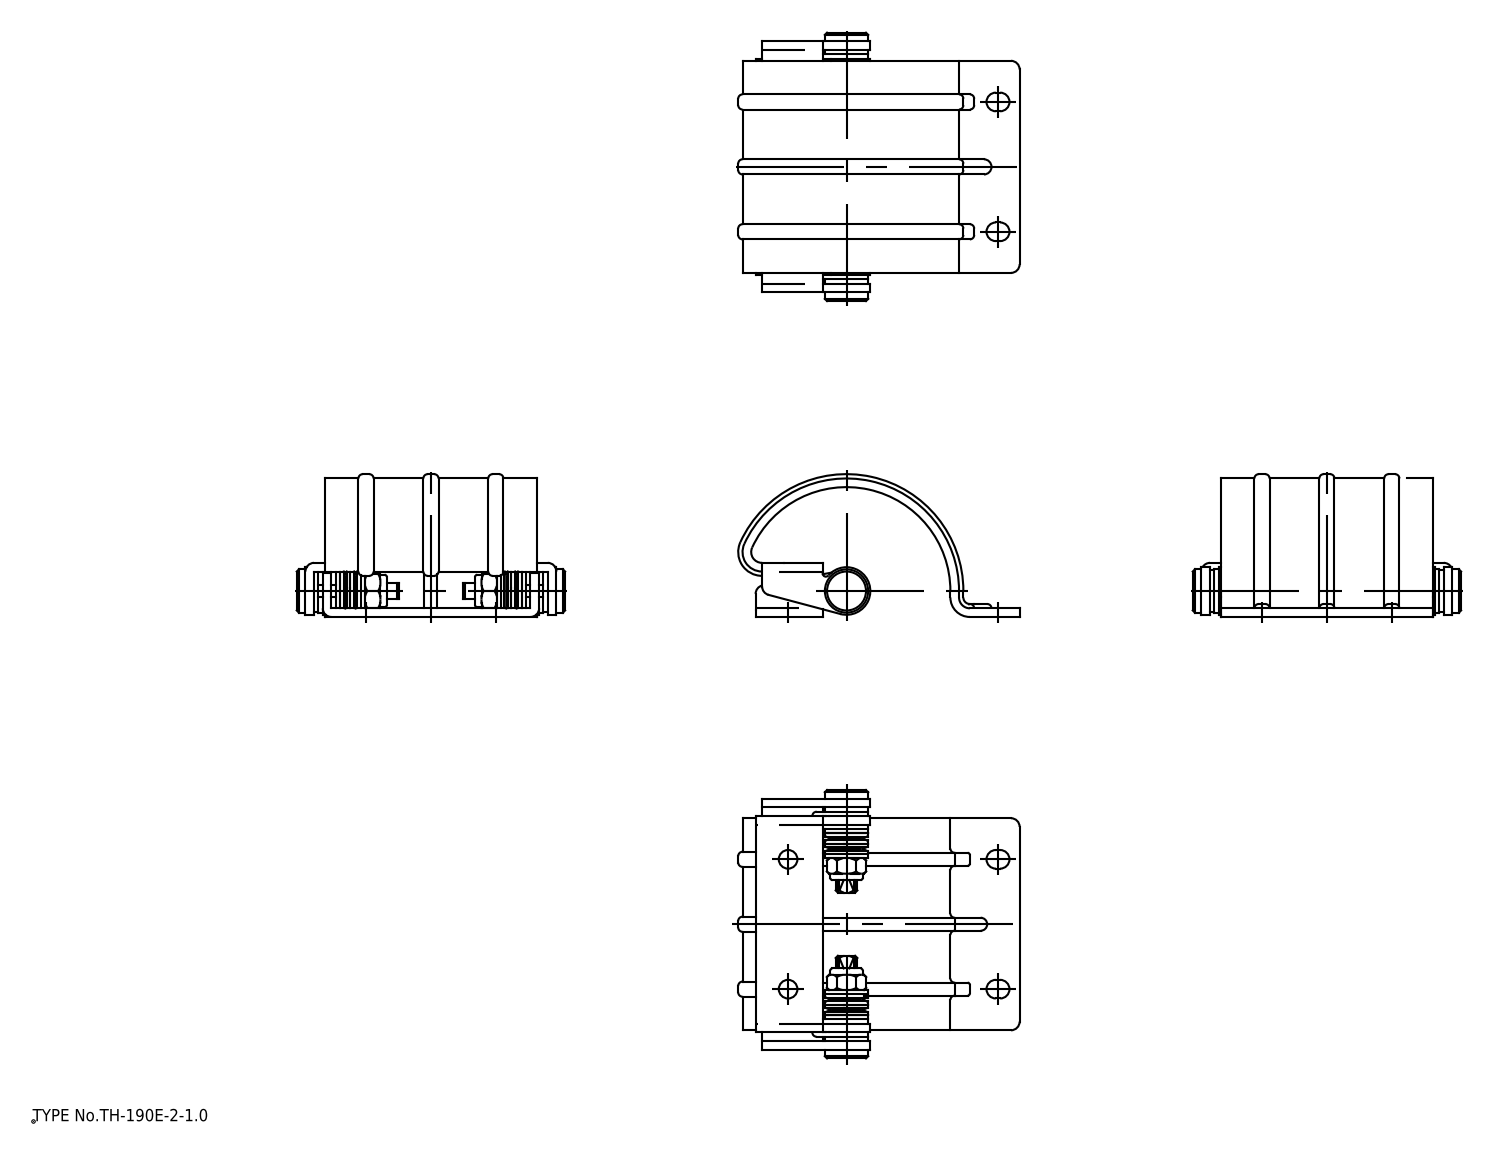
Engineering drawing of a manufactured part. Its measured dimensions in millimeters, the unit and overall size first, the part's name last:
Units: millimetres
Overall size (bounding box): 65.03 × 62 × 33
Round holes (diameter × count): ⌀4.3 ×2
Round bosses / shafts (diameter × count): ⌀10 ×1, ⌀9.9 ×1, ⌀9.8 ×1, ⌀7.5 ×1
Partial cylindrical surfaces — rounded edges, fillets, slot ends (radius × count): R1 ×37, R2 ×8, R0.75 ×7, R0.5 ×4, R2.15 ×4, R2.5 ×3, R3.5 ×2, R4.5 ×2
Main face-to-face distances: 2, 10.5, 1, 4, 3, 49, 8.5, 52, 1.5, 12.5
Hole centre spacings: 30
Volume: 16 167 mm³ · Surface area: 17 385 mm²
Bodies: 2 solids, 426 faces (116 planar, 172 cylindrical, 138 other)
Part name (STEP PRODUCT): ヒンジピース(A); ヒンジピース(B)
STEP written by: spGate 20.6.3 (****-****-****-****) (AUTOMOTIVE_DESIGN)
